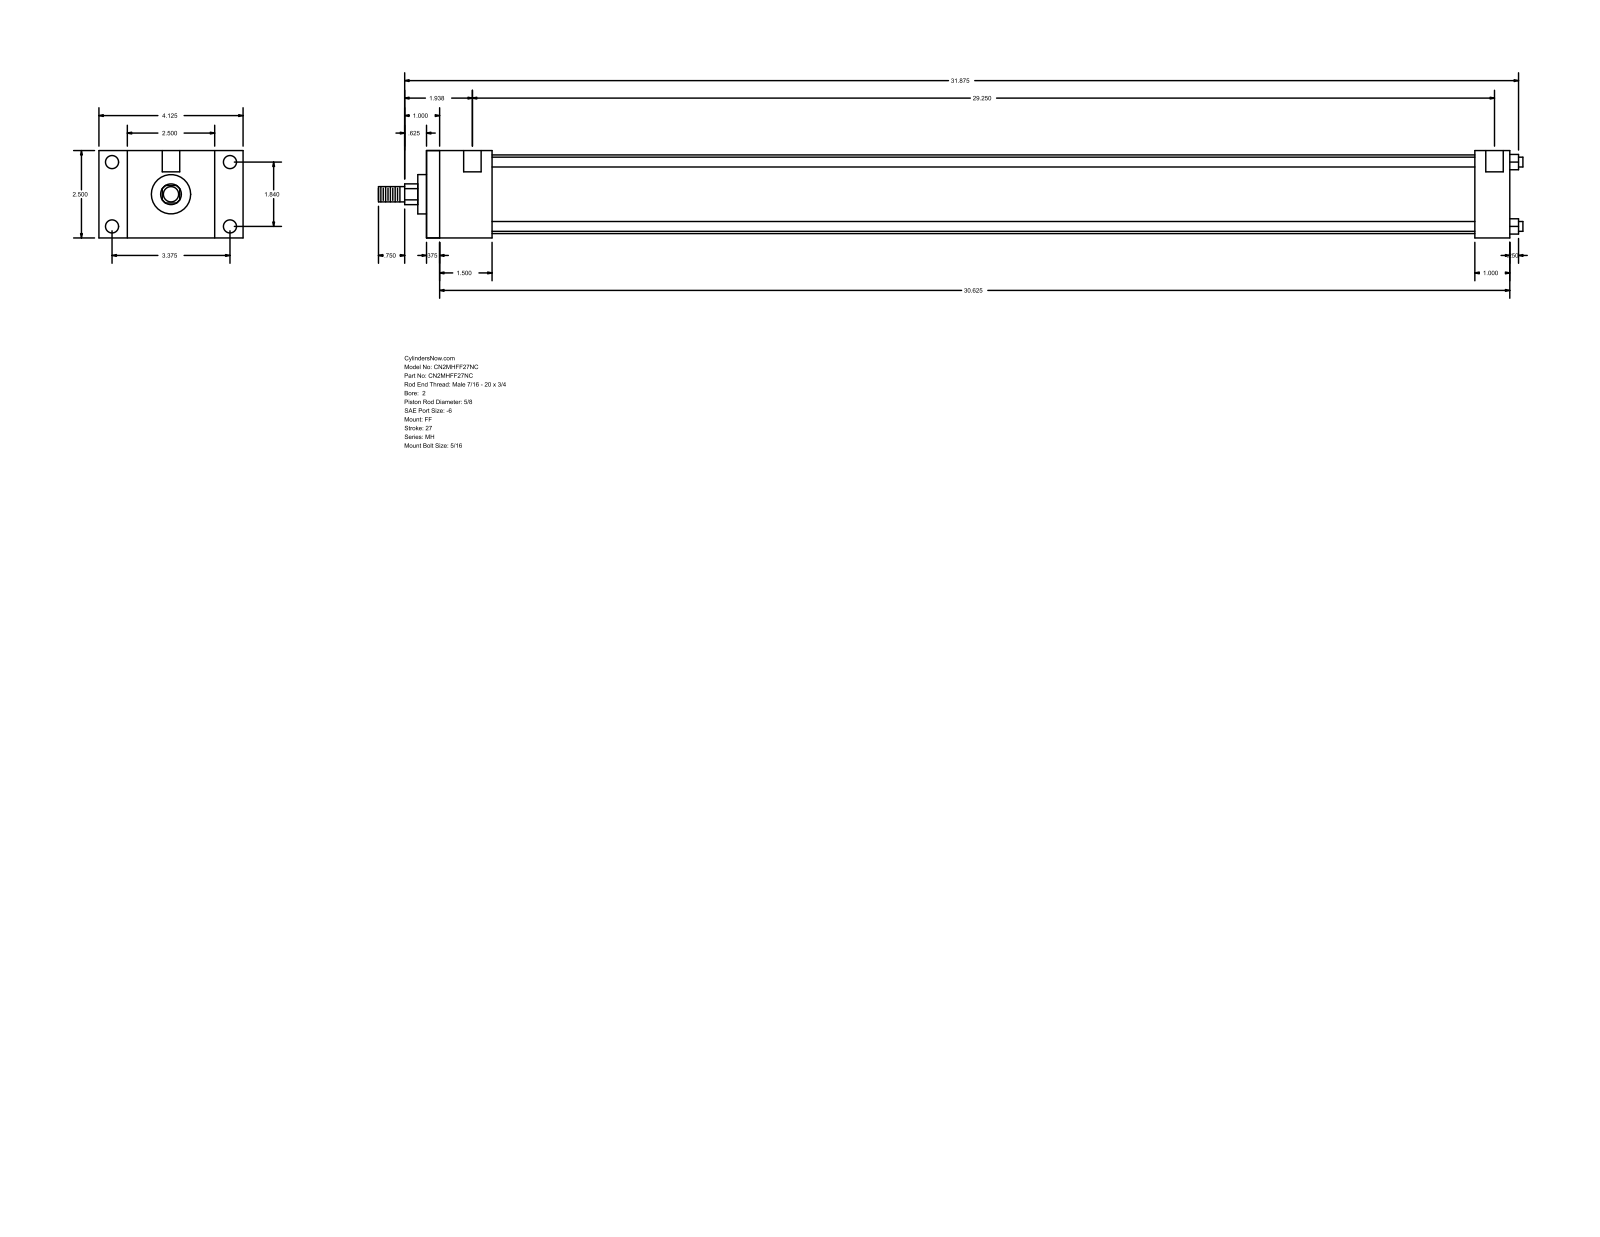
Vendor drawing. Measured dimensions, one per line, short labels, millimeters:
name: MH_FF__0200_0.625
written by: GSSL Pune (CONFIG_CONTROL_DESIGN)
unit: mm
bodies: 0 solids, 92 faces (64 planar, 28 cylindrical, 0 other)
size: 831.85 × 104.78 × 63.5
holes: 4× ⌀5.56, 4× ⌀9.53, 2× ⌀12.7
bosses: 4× ⌀7.14, 1× ⌀57.15, 1× ⌀28.57, 1× ⌀15.88, 1× ⌀11.11
rounds: 1× R7.54
face distances: 63.5, 787.39, 9.52, 777.87, 38.1, 47.62, 762, 752.48, 714.38, 739.77
hole spacings: 46.74, 85.72, 97.63, 750.89, 3.18, 4.76, 742.95, 746.13
